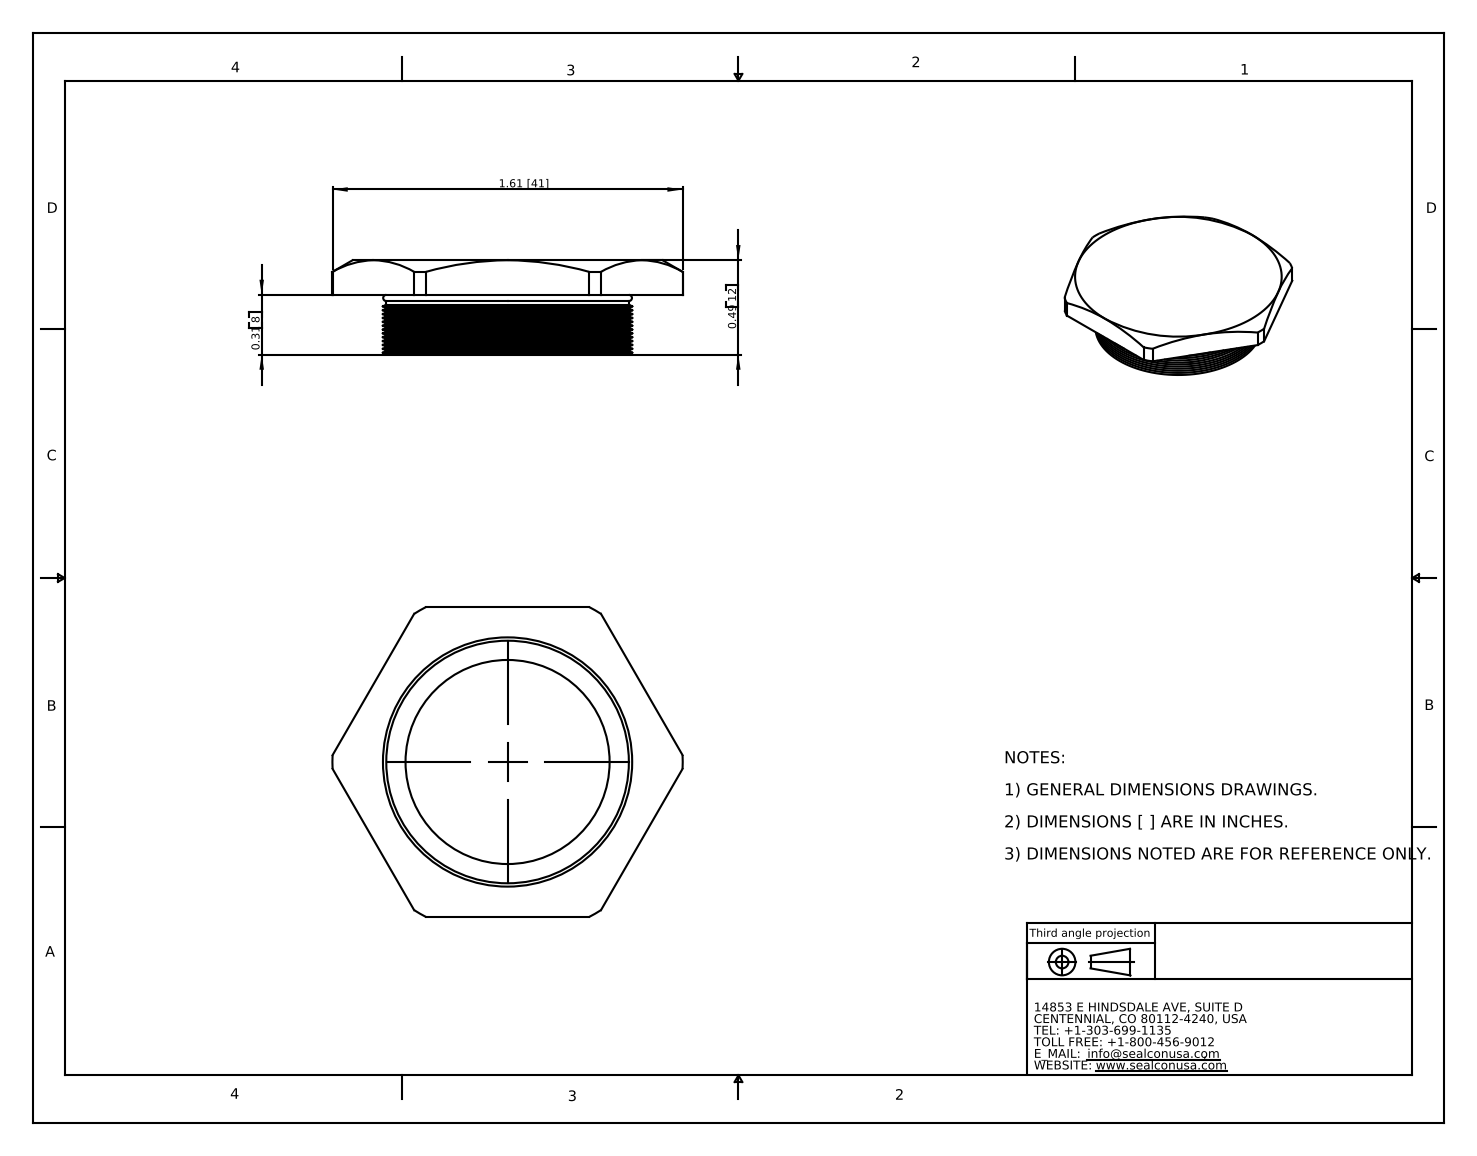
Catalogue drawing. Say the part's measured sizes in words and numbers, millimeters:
The part is named "HM-32-SS-B". Its 3-D file was written by "SolidWorks 2007 (CONFIG_CONTROL_DESIGN)". It is 1 solid with 80 faces: 10 planar, 10 cylindrical and 60 other. Overall it measures 46.2 by 40.9 by 12.4 millimeters. Its volume is 8 570 cubic millimeters and its surface area 5 656 square millimeters. Round holes: 1 of diameter 26.9. Round bosses or shafts: 1 of diameter 32. Partial cylindrical surfaces (rounded edges, fillets, slot ends): 1 of radius 23.1. The main face-to-face distances are 4.6, 40.9, 7.9, 12.4.
